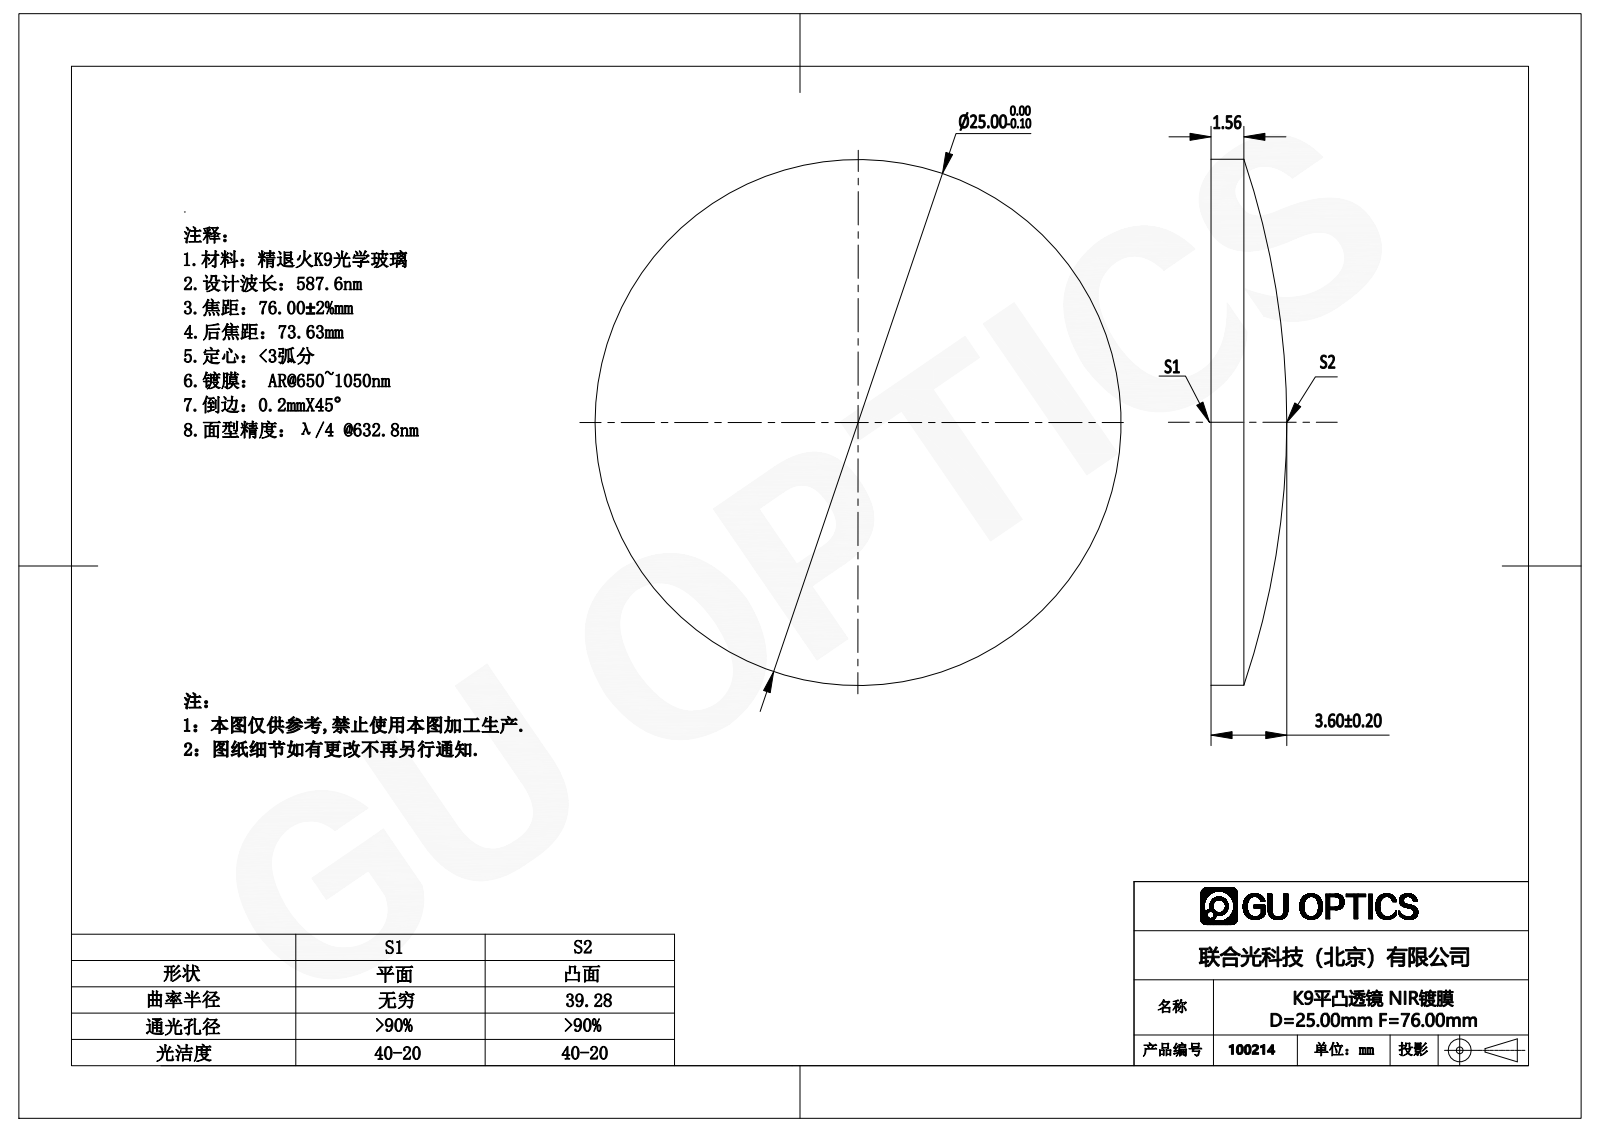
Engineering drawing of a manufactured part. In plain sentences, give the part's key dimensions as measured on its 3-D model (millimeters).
The part is named "100214". Its 3-D file was written by "SolidWorks 2016 (AUTOMOTIVE_DESIGN)". It is 1 solid with 5 faces: 1 planar, 2 cylindrical and 2 other. Overall it measures 25 by 25 by 3.6 millimeters. Its volume is 1 271 cubic millimeters and its surface area 1 117 square millimeters. Round bosses or shafts: 1 of diameter 25.
